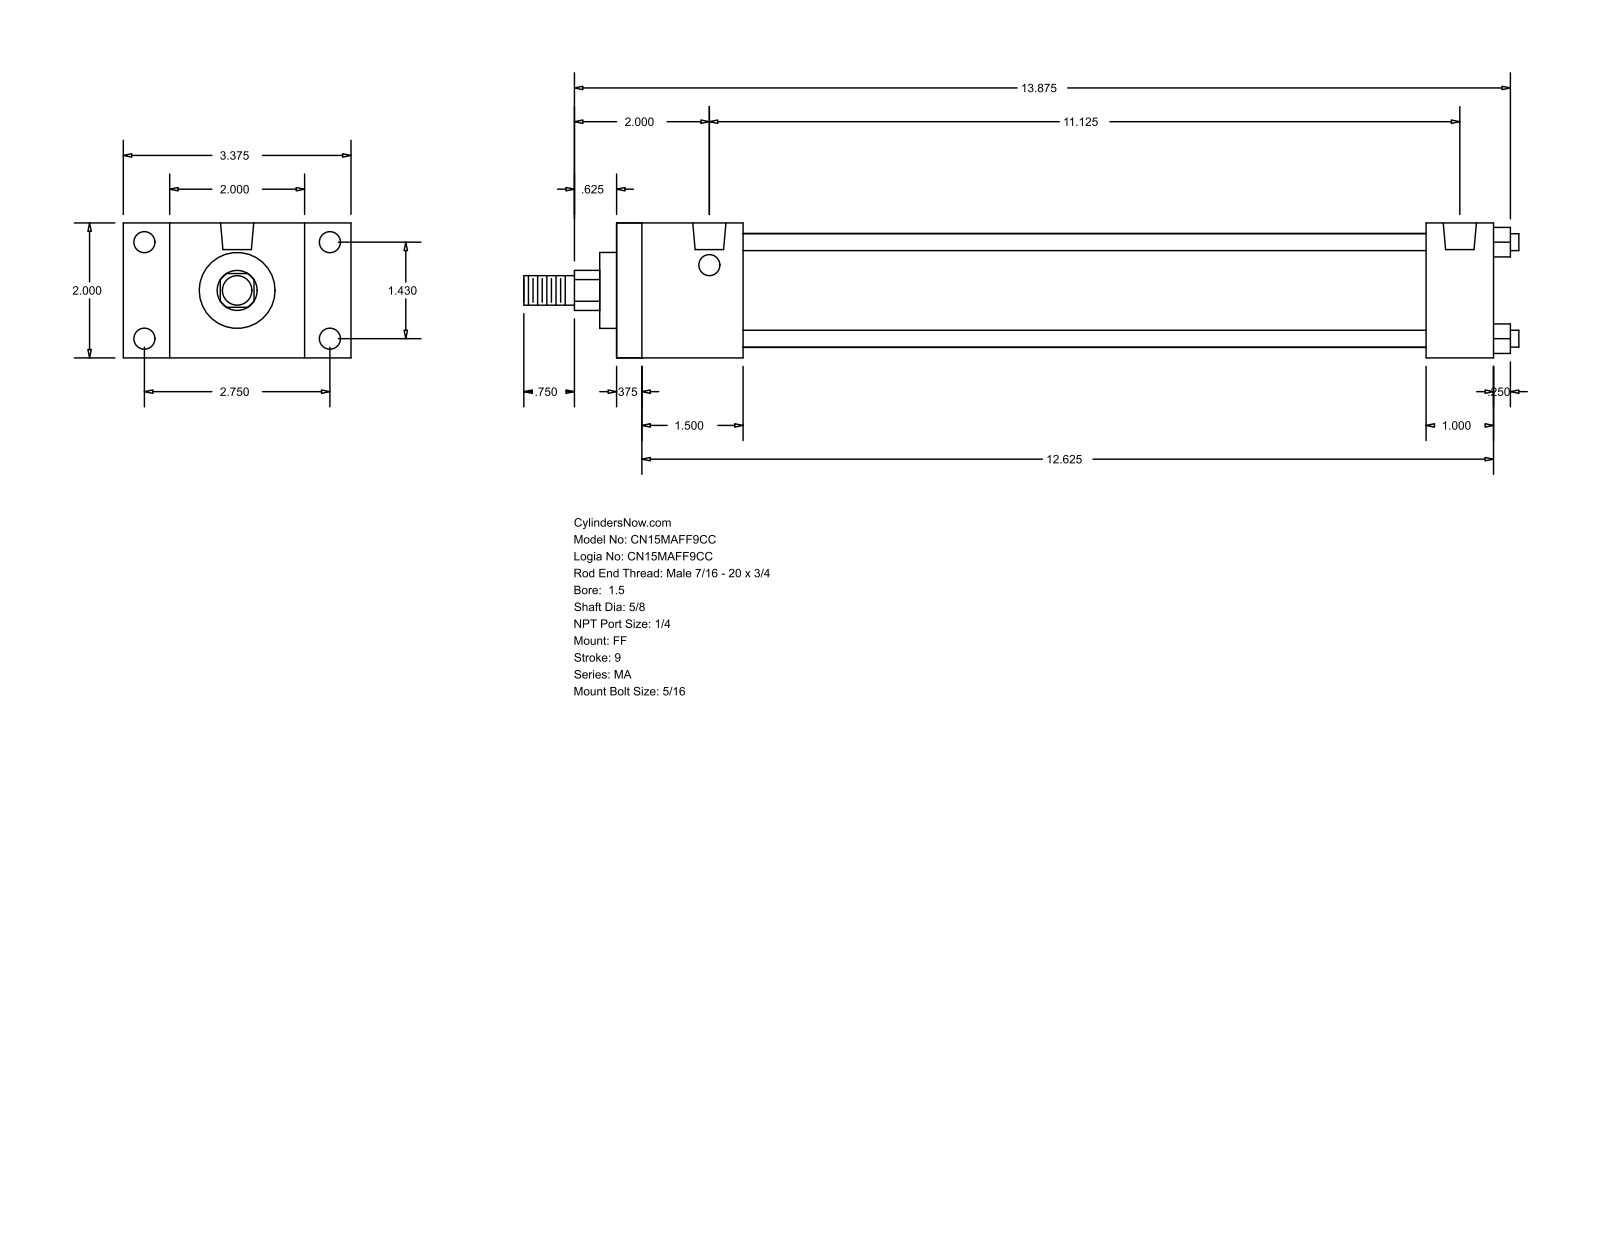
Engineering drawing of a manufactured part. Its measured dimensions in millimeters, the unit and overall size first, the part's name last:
Units: millimetres
Overall size (bounding box): 374.65 × 85.72 × 50.8
Round holes (diameter × count): ⌀7.94 ×8, ⌀12.49 ×2
Round bosses / shafts (diameter × count): ⌀6.35 ×4, ⌀42.93 ×1, ⌀28.57 ×1, ⌀15.88 ×1, ⌀11.11 ×1
Partial cylindrical surfaces — rounded edges, fillets, slot ends (radius × count): R7.54 ×1
Main face-to-face distances: 50.8, 330.19, 9.52, 320.67, 47.62, 304.8, 38.1, 295.28, 257.18, 282.57
Hole centre spacings: 36.32, 69.84, 78.72, 282.58
Bodies: 0 solids, 92 faces (64 planar, 28 cylindrical, 0 other)
Part name (STEP PRODUCT): MA_FF__0150_0.625
STEP written by: GSSL Pune (CONFIG_CONTROL_DESIGN)
